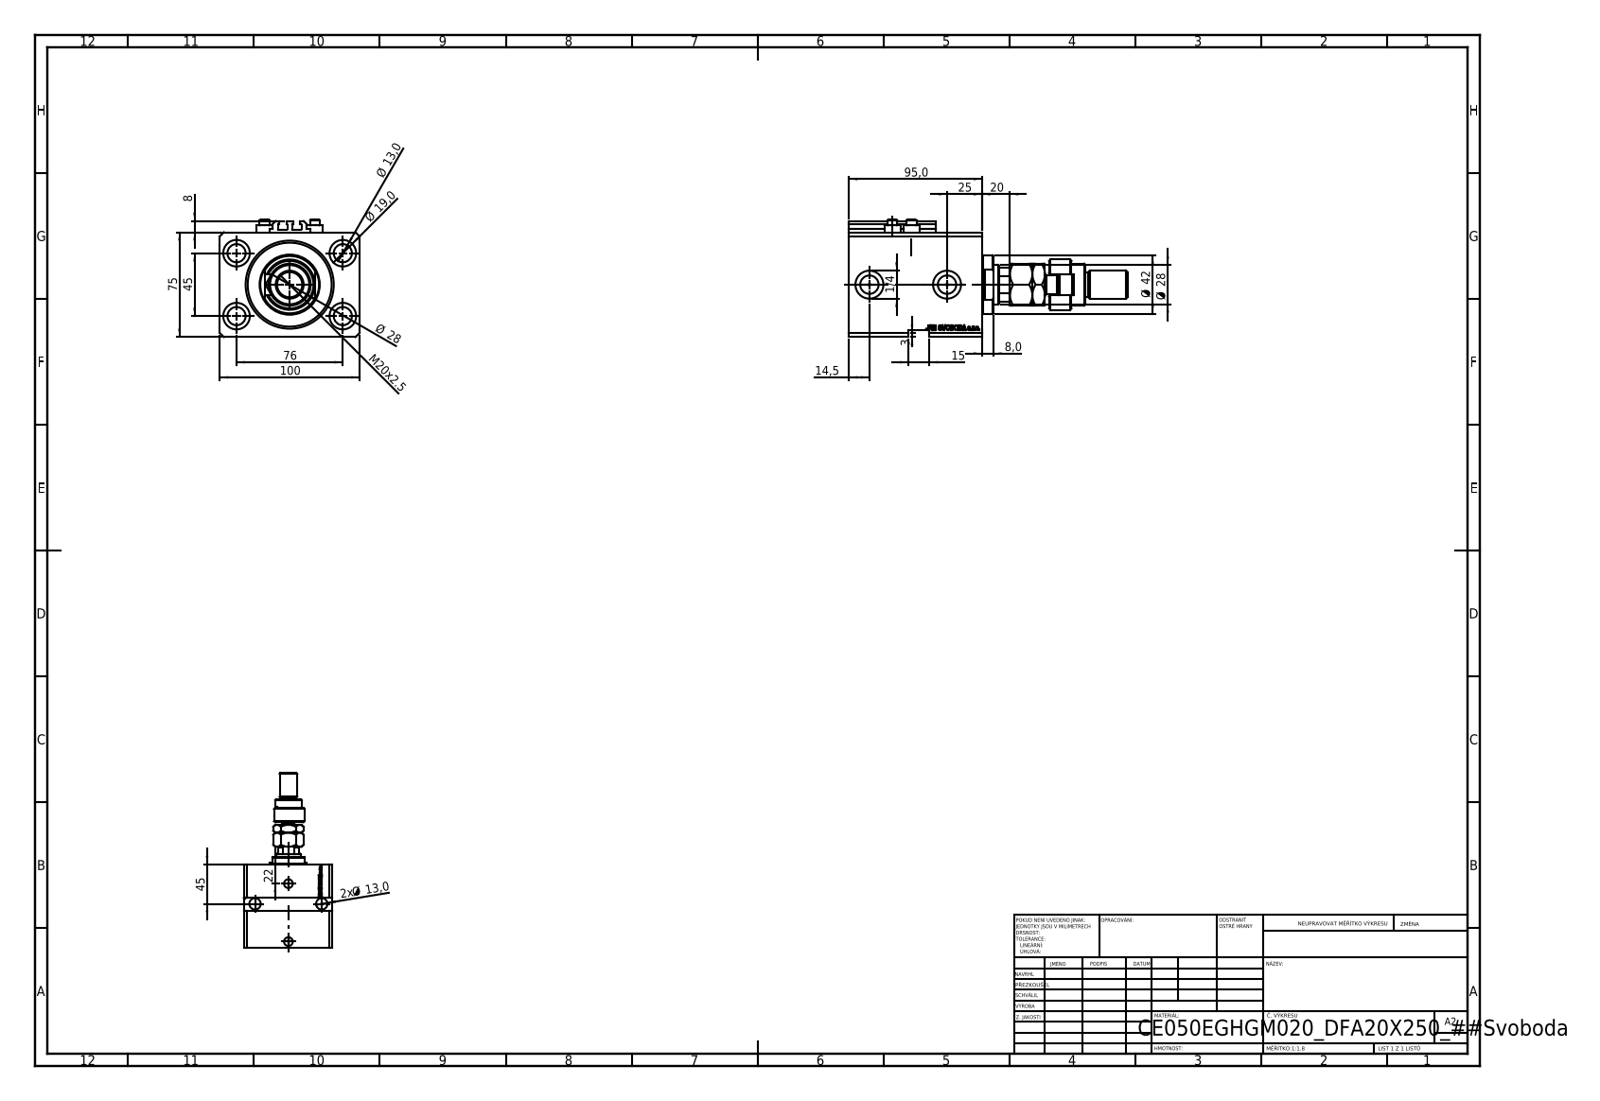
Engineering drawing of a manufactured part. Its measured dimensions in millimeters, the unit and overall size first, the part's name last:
Units: millimetres
Overall size (bounding box): 199 × 100 × 84
Round holes (diameter × count): ⌀13 ×6, ⌀1.25 ×4, ⌀4 ×4, ⌀19 ×4, ⌀10 ×2, ⌀13.16 ×2, ⌀20 ×2, ⌀18.5 ×1, ⌀28 ×1, ⌀50 ×1, ⌀63 ×1
Round bosses / shafts (diameter × count): ⌀11.6 ×4, ⌀7 ×4, ⌀42 ×1, ⌀36 ×1, ⌀30 ×1, ⌀22 ×1, ⌀20 ×1, ⌀18 ×1
Partial cylindrical surfaces — rounded edges, fillets, slot ends (radius × count): R0.2 ×10, R7.5 ×1, R12 ×1, R13.5 ×1
Main face-to-face distances: 75, 20, 100, 95, 11.9, 83.1, 63.1, 40, 30, 57.5
Hole centre spacings: 44.16, 76, 13.6, 20.72, 27.59, 29.58, 30, 33.62
Volume: 659 897 mm³ · Surface area: 135 136 mm²
Bodies: 10 solids, 1173 faces (563 planar, 139 cylindrical, 471 other)
Part name (STEP PRODUCT): FEMALE_PART_FOR_DFA; ALLEN BOLT V250CE; MFA; V250CE_C_VCP (+2 more)
STEP written by: SolidWorks 2019 (CONFIG_CONTROL_DESIGN)
